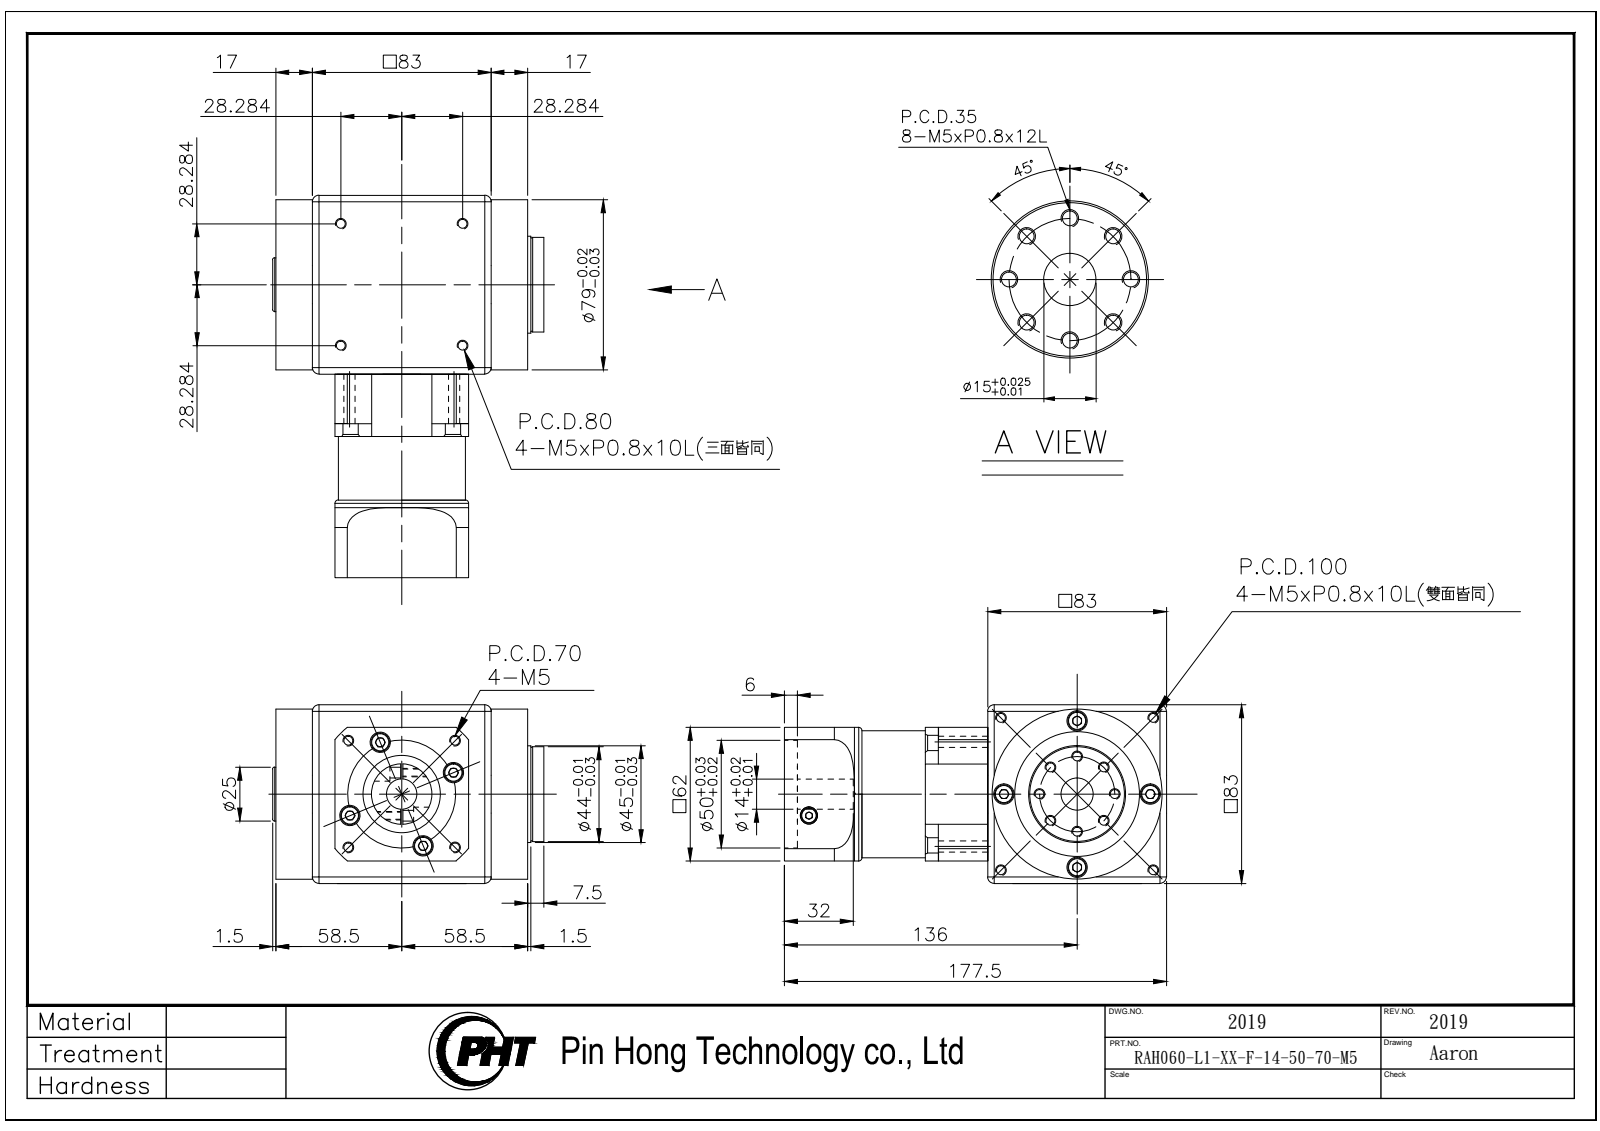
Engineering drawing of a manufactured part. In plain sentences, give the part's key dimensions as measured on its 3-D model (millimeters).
The part is named "RAH060-L1-XX-F-14-50-70-M5_2019". Its 3-D file was written by "SolidWorks 2016 (AUTOMOTIVE_DESIGN)". It is 2 solids with 609 faces: 258 planar, 221 cylindrical and 130 other. Overall it measures 177.5 by 126 by 83 millimeters. Its volume is 1 002 000 cubic millimeters and its surface area 110 968 square millimeters. Round holes: 24 of diameter 4.2, 8 of diameter 5.2, 8 of diameter 9.5, 4 of diameter 5.5, 2 of diameter 8, 1 of diameter 14, 1 of diameter 15, 1 of diameter 15.6, 1 of diameter 36. Round bosses or shafts: 12 of diameter 8.5, 1 of diameter 79, 1 of diameter 61.8, 1 of diameter 59, 1 of diameter 58, 1 of diameter 55, 1 of diameter 45, 1 of diameter 44. Partial cylindrical surfaces (rounded edges, fillets, slot ends): 4 of radius 5, 1 of radius 25, 1 of radius 34, 1 of radius 40, 1 of radius 57.15. The main face-to-face distances are 83, 10.5, 72.5, 62, 89.5, 27.5, 17, 100, 2, 81. The hole center spacings are 13.39, 32.33, 39.61, 52.98, 53.15, 56.56, 63.6, 35.
